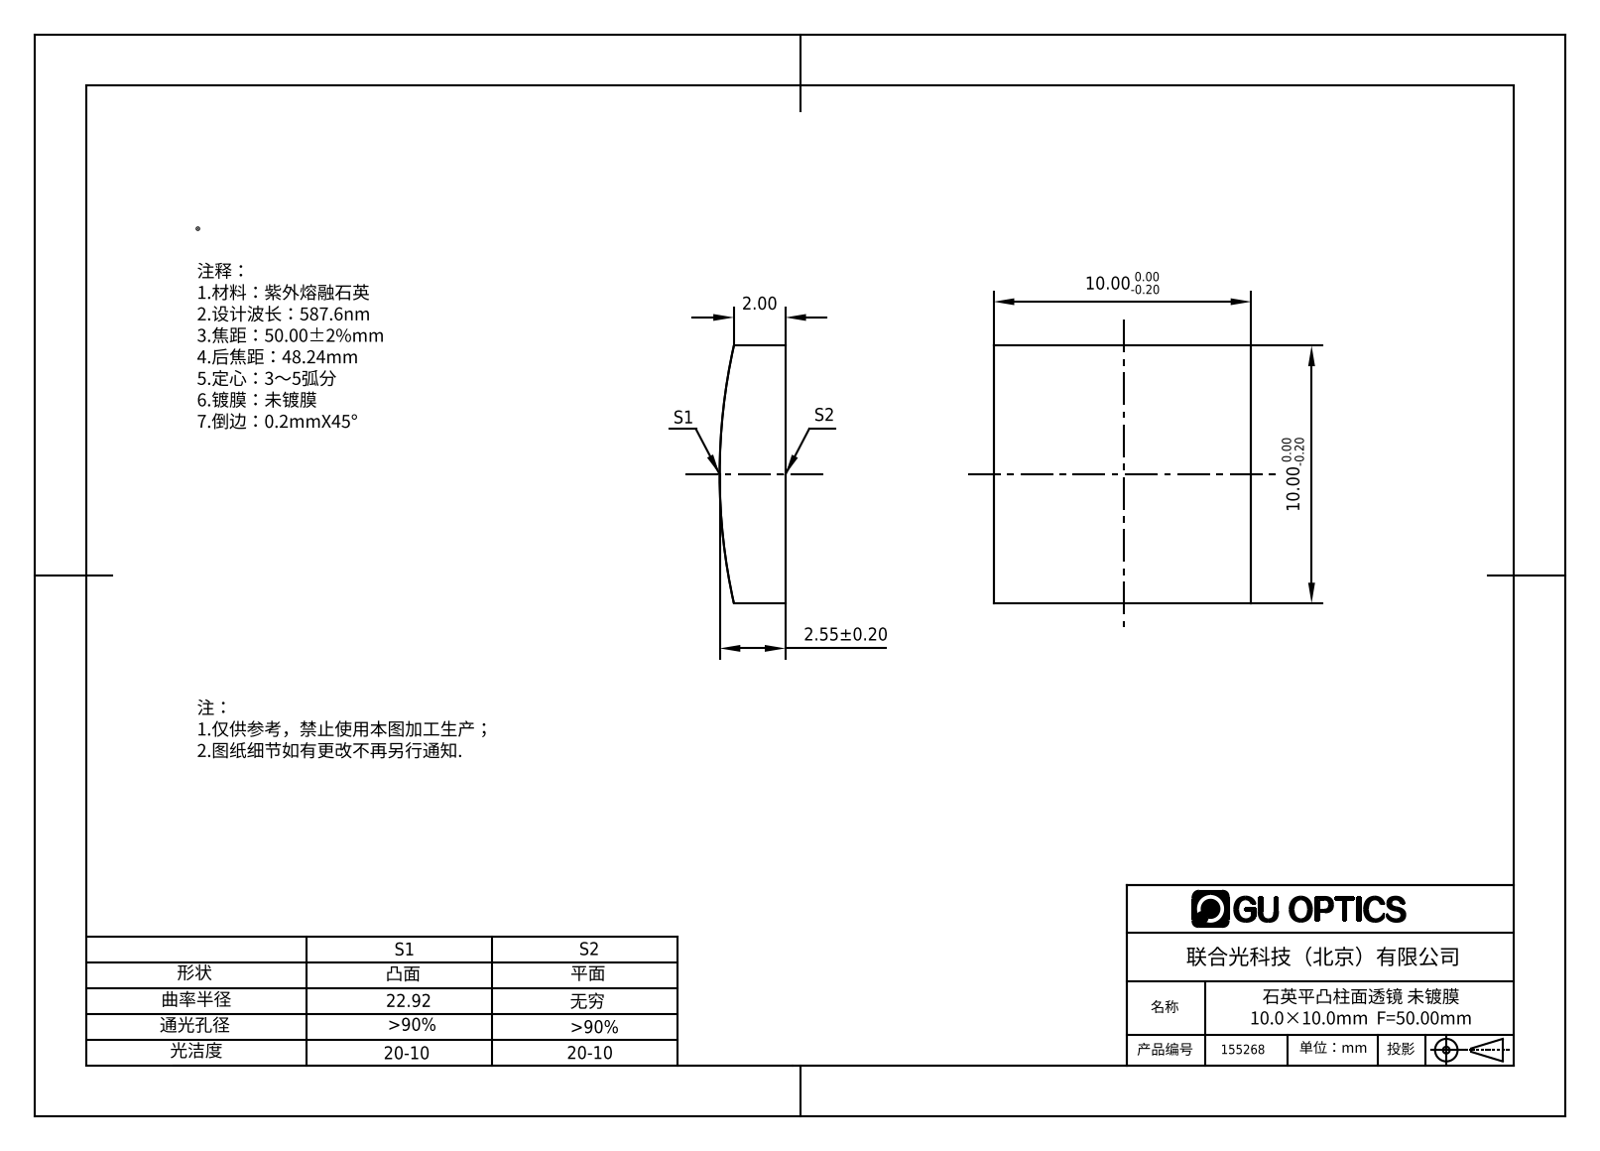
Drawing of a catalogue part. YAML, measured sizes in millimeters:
part_name: "155268"
step_written_by: "SolidWorks 2016 (AUTOMOTIVE_DESIGN)"
units: millimeters
bodies: {solids: 1, faces: 6, planar: 5, cylindrical: 1, other: 0}
overall_size: [10, 10, 2.55]
volume: 237
surface_area: 288
partial_cylinders:
  - {radius: 22.92, count: 1}
face_to_face_distances: [10]
